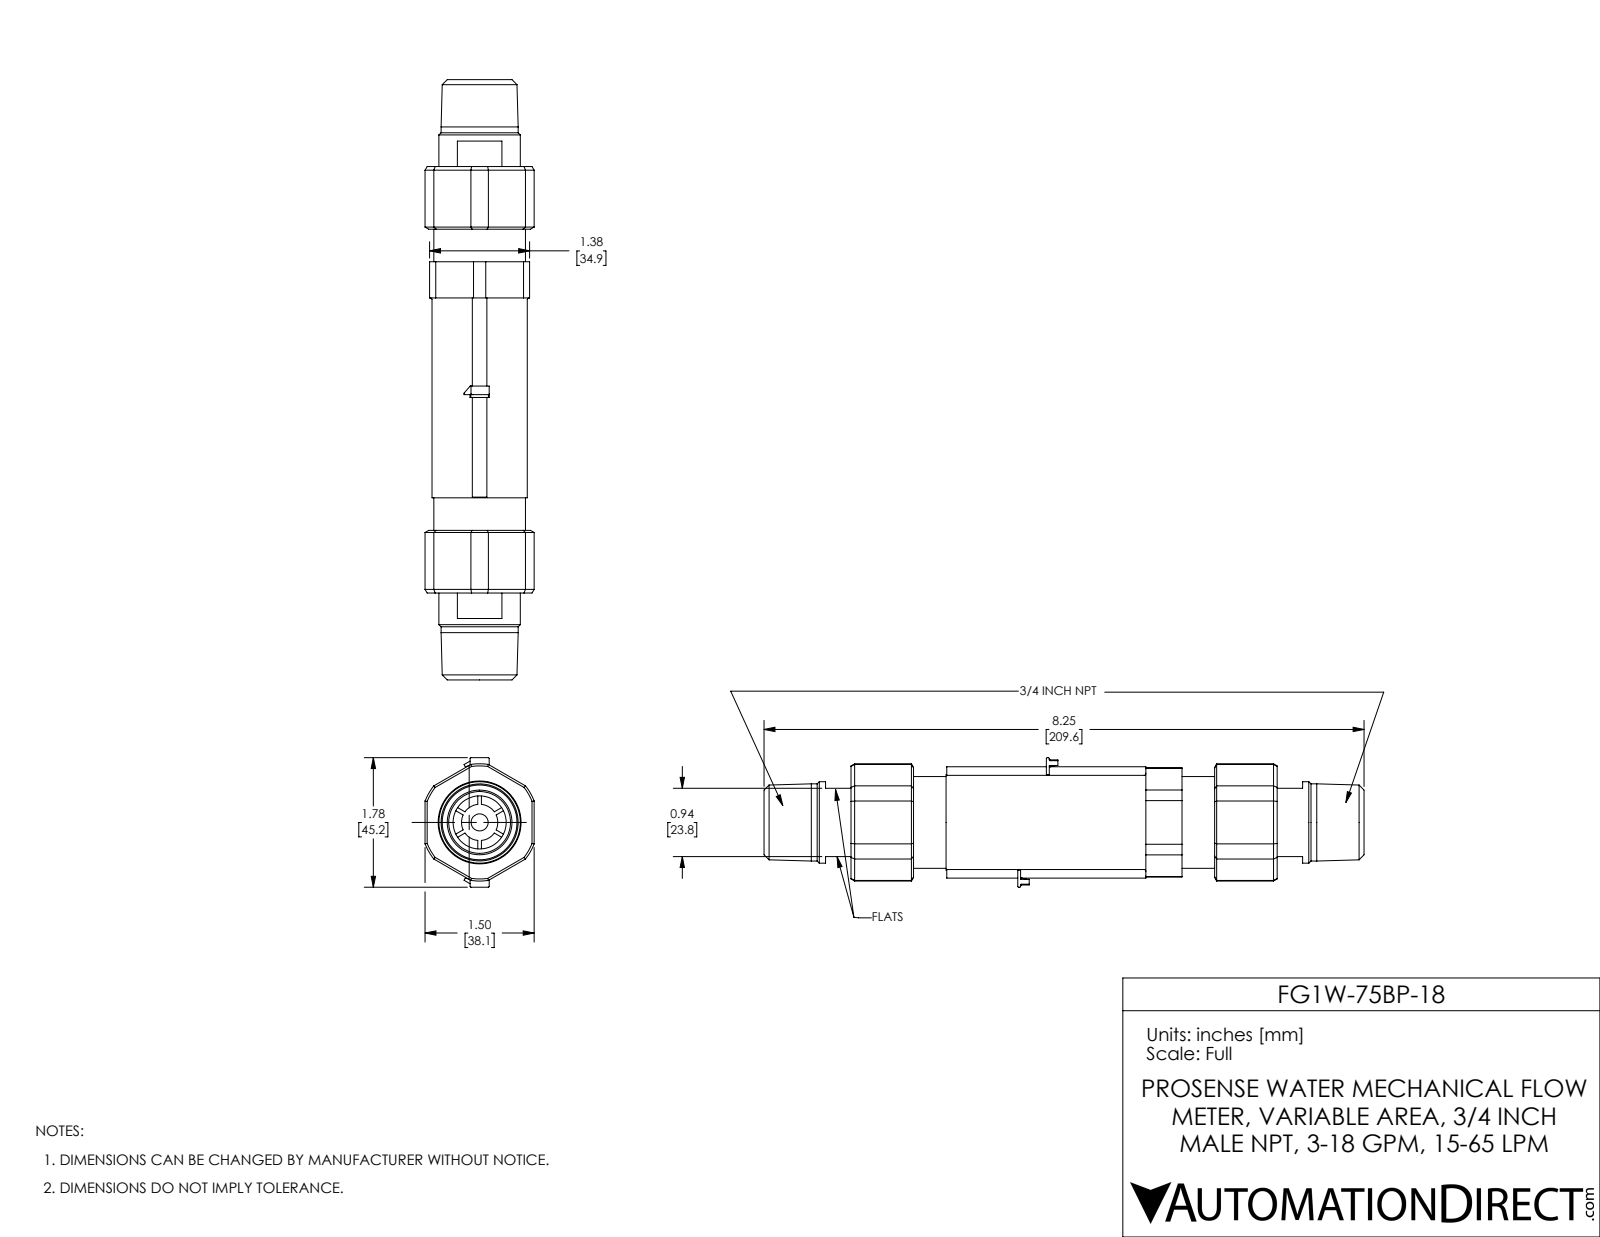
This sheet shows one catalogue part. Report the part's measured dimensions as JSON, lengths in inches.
{"part_name": "FG1P-75BP-2", "step_written_by": "SolidWorks 2017 (AUTOMOTIVE_DESIGN)", "units": "inches", "bodies": {"solids": 5, "faces": 412, "planar": 148, "cylindrical": 167, "other": 97}, "overall_size": [8.25, 1.78, 1.5], "volume_in3": 6.101, "surface_area_in2": 96.24, "round_holes": [[0.73, 1], [0.97, 1], [1.14, 1], [1.286, 1]], "round_bosses_or_shafts": [[1.373, 1], [1.31, 1], [1.26, 1], [1.25, 1], [1.12, 1], [1.06, 1], [1.036, 1], [0.498, 1]], "partial_cylinders_radius": [[0.012, 12], [0.02, 12], [0.005, 4], [0.67, 3], [0.75, 3], [0.806, 1]], "face_to_face_distances": [1.5, 0.063, 1.437, 0.65, 0.85, 0.296, 1.234, 1.375, 0.725, 0.775]}
